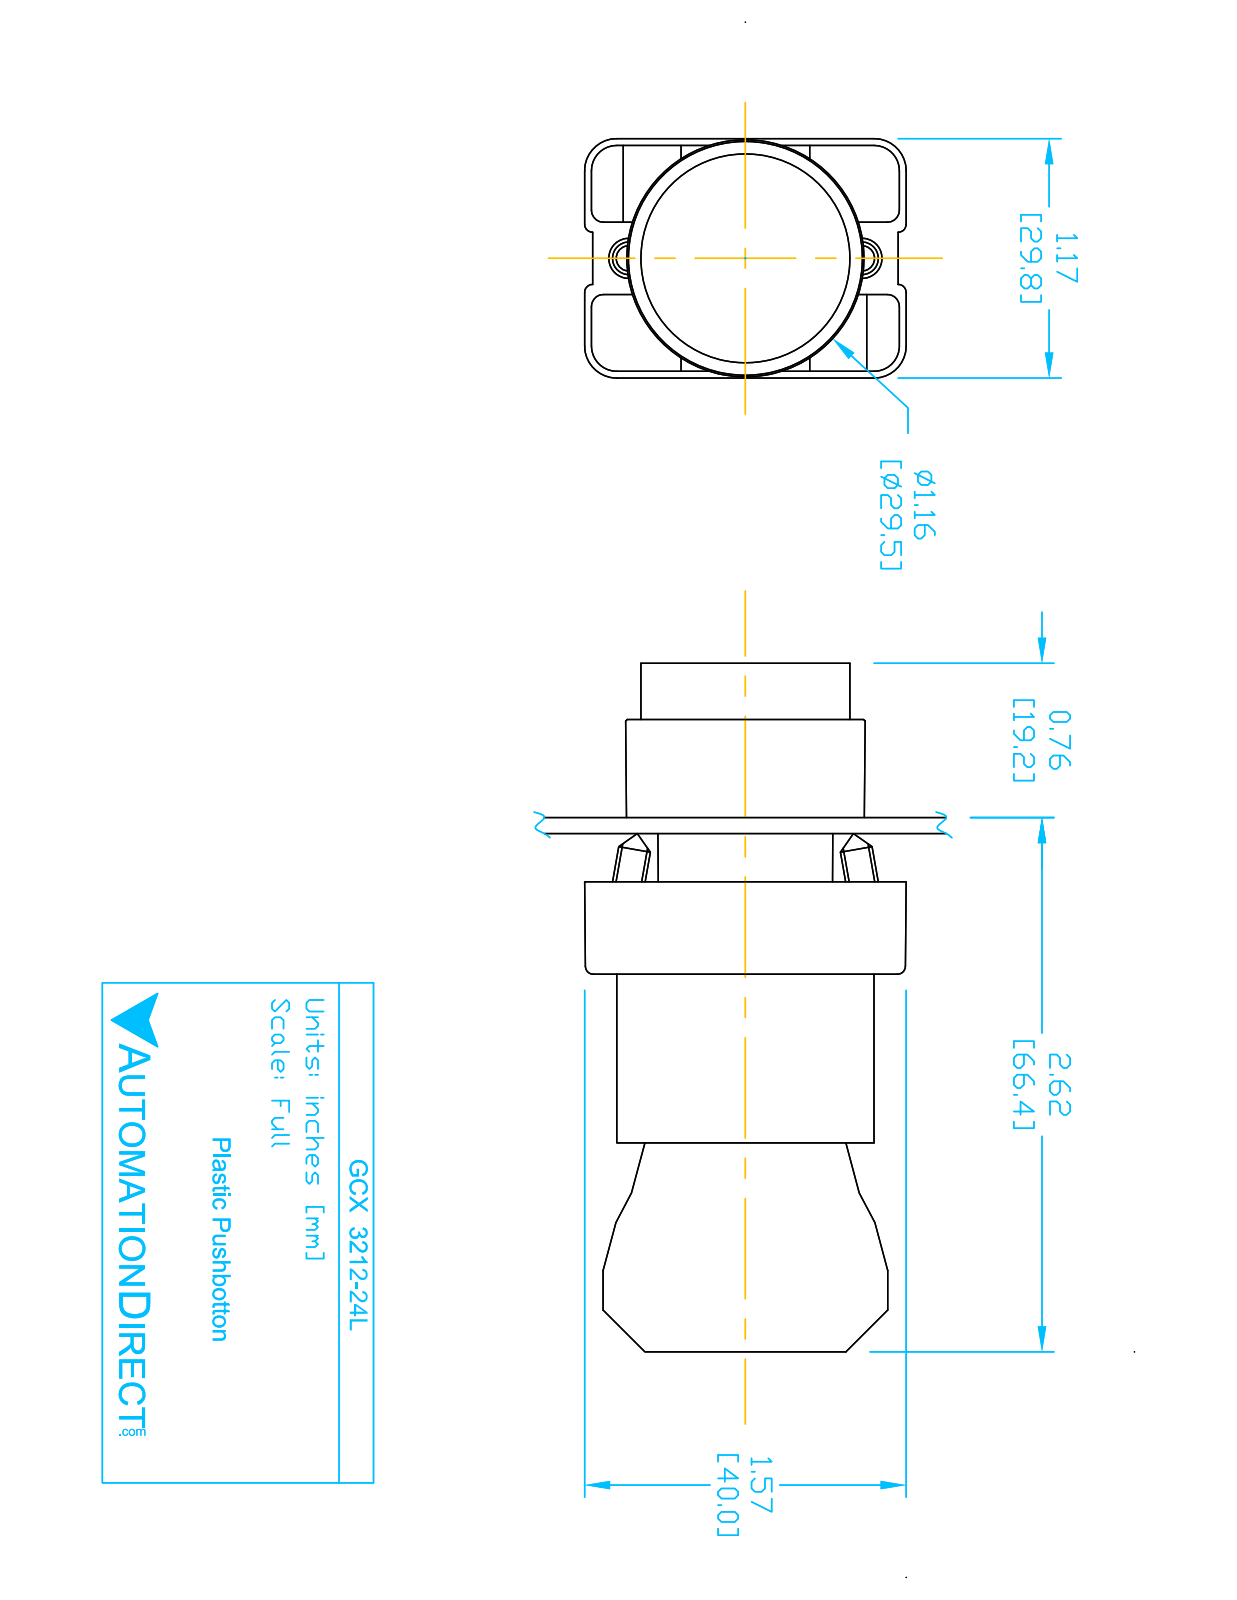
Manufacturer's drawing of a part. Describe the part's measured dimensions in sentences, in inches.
The part is named "GCX3212L OPERATOR; ECX1050; ecx1040; ECX3029-2 (+1 more)". Its 3-D file was written by "SolidWorks 2016 (AUTOMOTIVE_DESIGN)". It is 7 solids with 425 faces: 250 planar, 144 cylindrical and 31 other. Overall it measures 3.319 by 1.581 by 1.177 inches. Its volume is 2.721 cubic inches and its surface area 36.32 square inches. Round holes: 2 of diameter 0.079, 2 of diameter 0.124, 2 of diameter 0.13, 1 of diameter 0.087, 1 of diameter 0.197, 1 of diameter 0.469, 1 of diameter 0.878, 1 of diameter 0.888, 1 of diameter 1.024. Round bosses or shafts: 4 of diameter 0.157, 1 of diameter 1.175, 1 of diameter 1.004, 1 of diameter 0.945, 1 of diameter 0.856, 1 of diameter 0.78, 1 of diameter 0.504. Partial cylindrical surfaces (rounded edges, fillets, slot ends): 24 of radius 0.059, 12 of radius 0.041, 12 of radius 0.124, 12 of radius 0.157, 8 of radius 0.039, 2 of radius 0.128, 1 of radius 0.02, 1 of radius 0.063. The main face-to-face distances are 0.827, 0.579, 1.171, 2.02, 1.193, 0.031, 0.033, 0.573, 1.165, 0.593. The hole center spacings are 0.236, 0.544, 0.472, 0.49.
